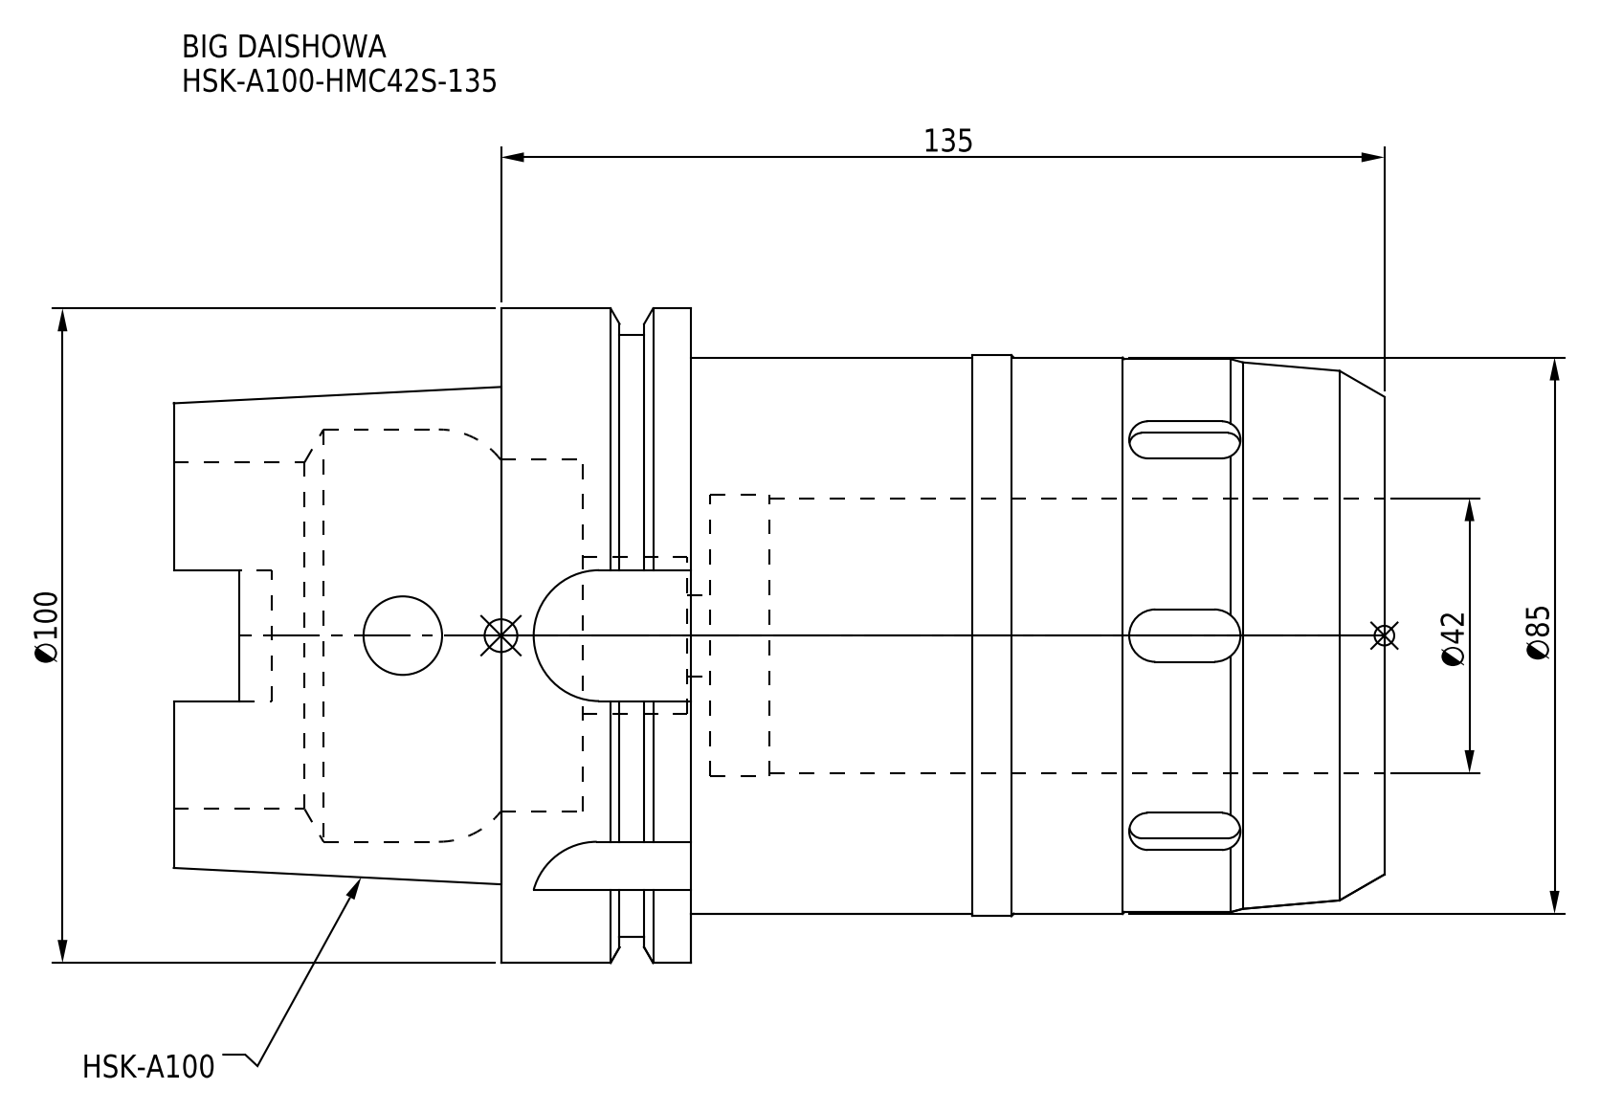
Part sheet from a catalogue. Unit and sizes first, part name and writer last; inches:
Units: inches
Overall size (bounding box): 7.283 × 3.937 × 3.937
Round holes (diameter × count): ⌀0.472 ×1, ⌀0.488 ×1, ⌀0.945 ×1, ⌀1.654 ×1, ⌀1.693 ×1, ⌀2.087 ×1, ⌀2.118 ×1, ⌀2.48 ×1
Round bosses / shafts (diameter × count): ⌀3.937 ×1, ⌀3.622 ×1, ⌀3.374 ×1, ⌀3.346 ×1, ⌀3.327 ×1
Partial cylindrical surfaces — rounded edges, fillets, slot ends (radius × count): R0.157 ×12, R0.192 ×4, R0.394 ×4
Main face-to-face distances: 5.315, 1.142, 4.173, 4.825, 0.652, 0.49, 1.969, 7.283, 3.11, 2.459
Volume: 42.48 in³ · Surface area: 141.7 in²
Bodies: 1 solid, 141 faces (59 planar, 60 cylindrical, 22 other)
Part name (STEP PRODUCT): HSK-A100-HMC42S-135
STEP written by: CREO PARAMETRIC BY PTC INC, 2016380 (AUTOMOTIVE_DESIGN)
